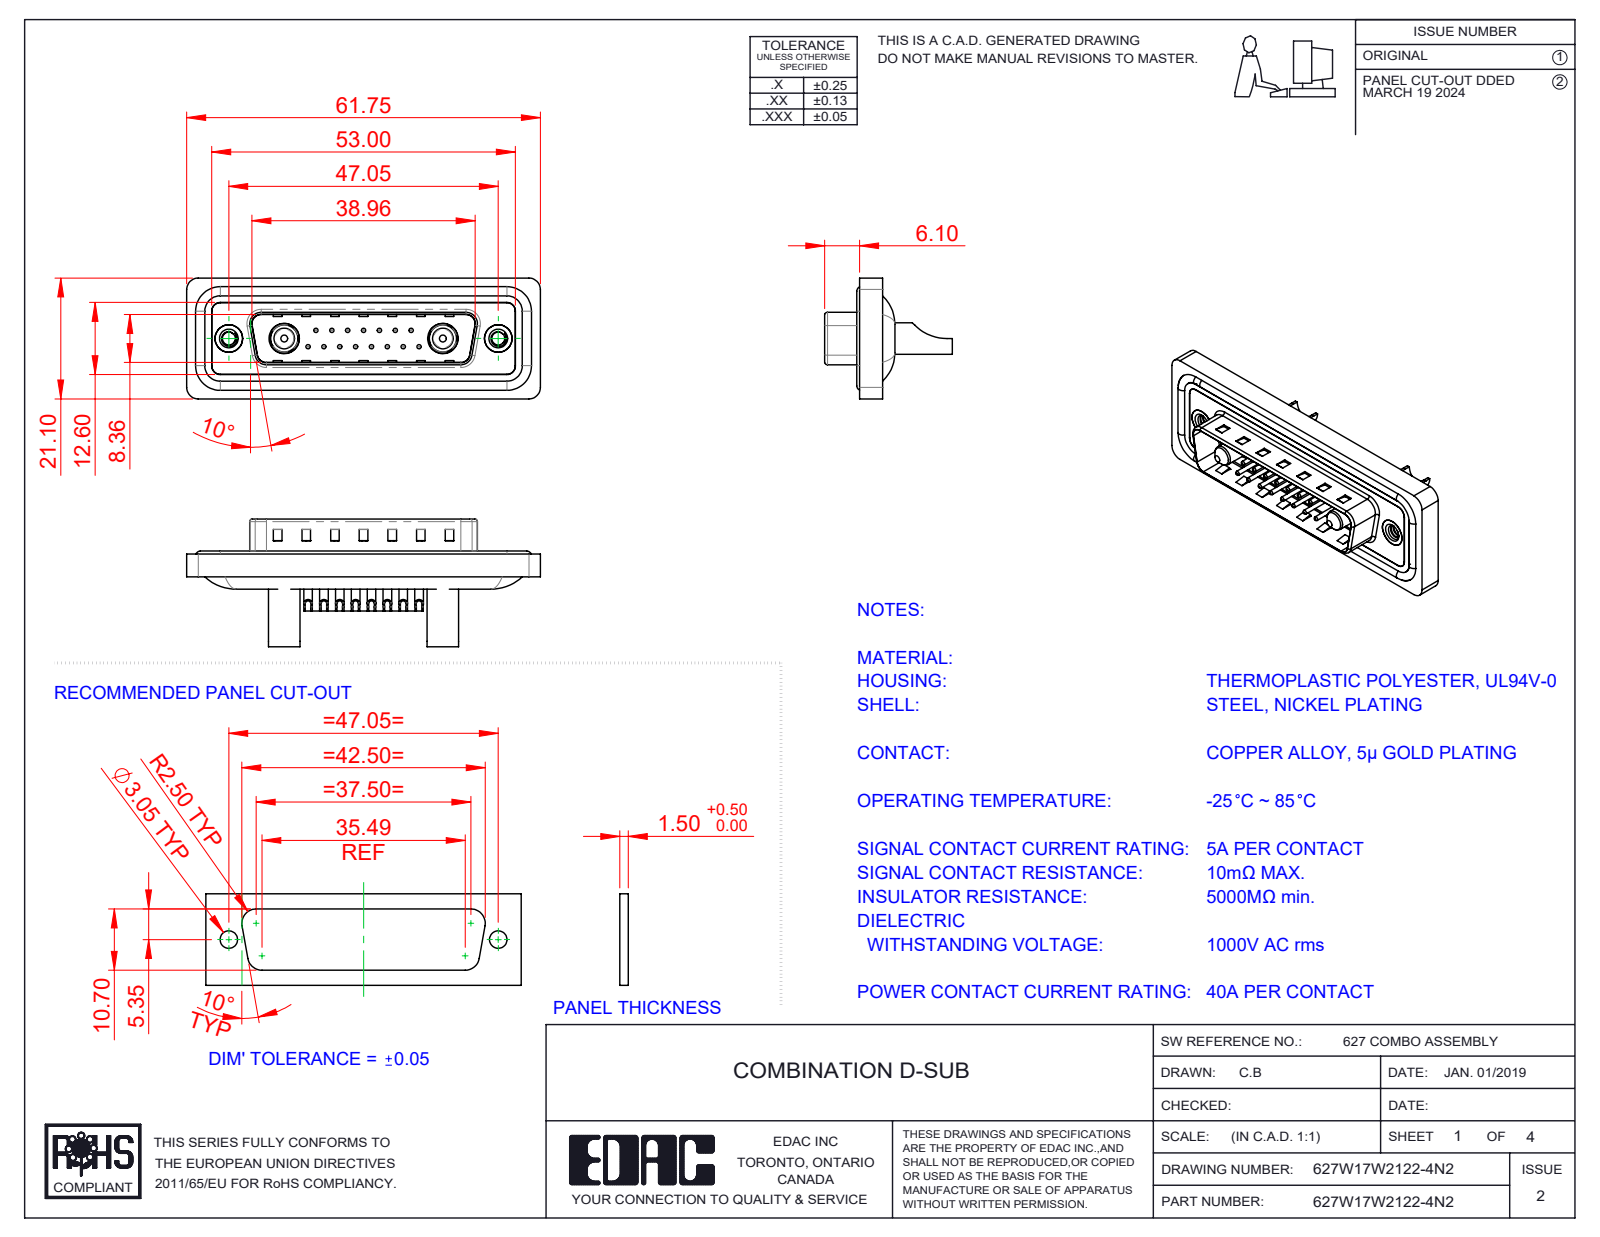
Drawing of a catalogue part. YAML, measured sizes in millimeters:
part_name: "627Combo Threaded Rivet_2; 627Combo Shell Front_25 Contacts; 627Combo Housing_17W2; Power Pin_40A SC (+5 more)"
step_written_by: "SolidWorks 2023 (CONFIG_CONTROL_DESIGN)"
units: millimeters
bodies: {solids: 26, faces: 1122, planar: 368, cylindrical: 468, other: 286}
overall_size: [61.75, 22.3, 21.1]
volume: 7369
surface_area: 12313
round_holes:
  - {diameter: 0.75, count: 15}
  - {diameter: 1, count: 15}
  - {diameter: 1.6, count: 15}
  - {diameter: 2, count: 15}
  - {diameter: 2.26, count: 2}
  - {diameter: 4, count: 2}
  - {diameter: 4.6, count: 2}
  - {diameter: 4.8, count: 2}
  - {diameter: 4.85, count: 2}
  - {diameter: 5, count: 2}
  - {diameter: 5.3, count: 2}
round_bosses_or_shafts:
  - {diameter: 1.5, count: 15}
  - {diameter: 1.6, count: 4}
  - {diameter: 5.5, count: 2}
  - {diameter: 5.2, count: 2}
  - {diameter: 4.9, count: 2}
  - {diameter: 4.75, count: 2}
  - {diameter: 3.75, count: 2}
  - {diameter: 3.6, count: 2}
partial_cylinders:
  - {radius: 1.5, count: 22}
  - {radius: 2, count: 18}
  - {radius: 0.5, count: 8}
  - {radius: 1.6, count: 8}
  - {radius: 1, count: 6}
  - {radius: 0.25, count: 4}
  - {radius: 0.6, count: 4}
  - {radius: 0.65, count: 4}
face_to_face_distances: [0.4, 1.5, 1.1, 1.6, 0.5, 3.1, 2.9, 0.82, 9.58, 4.1]
hole_center_spacings: [3.16, 2.77, 5.54, 8.31, 5.04, 7.49, 11.08, 5.03]
